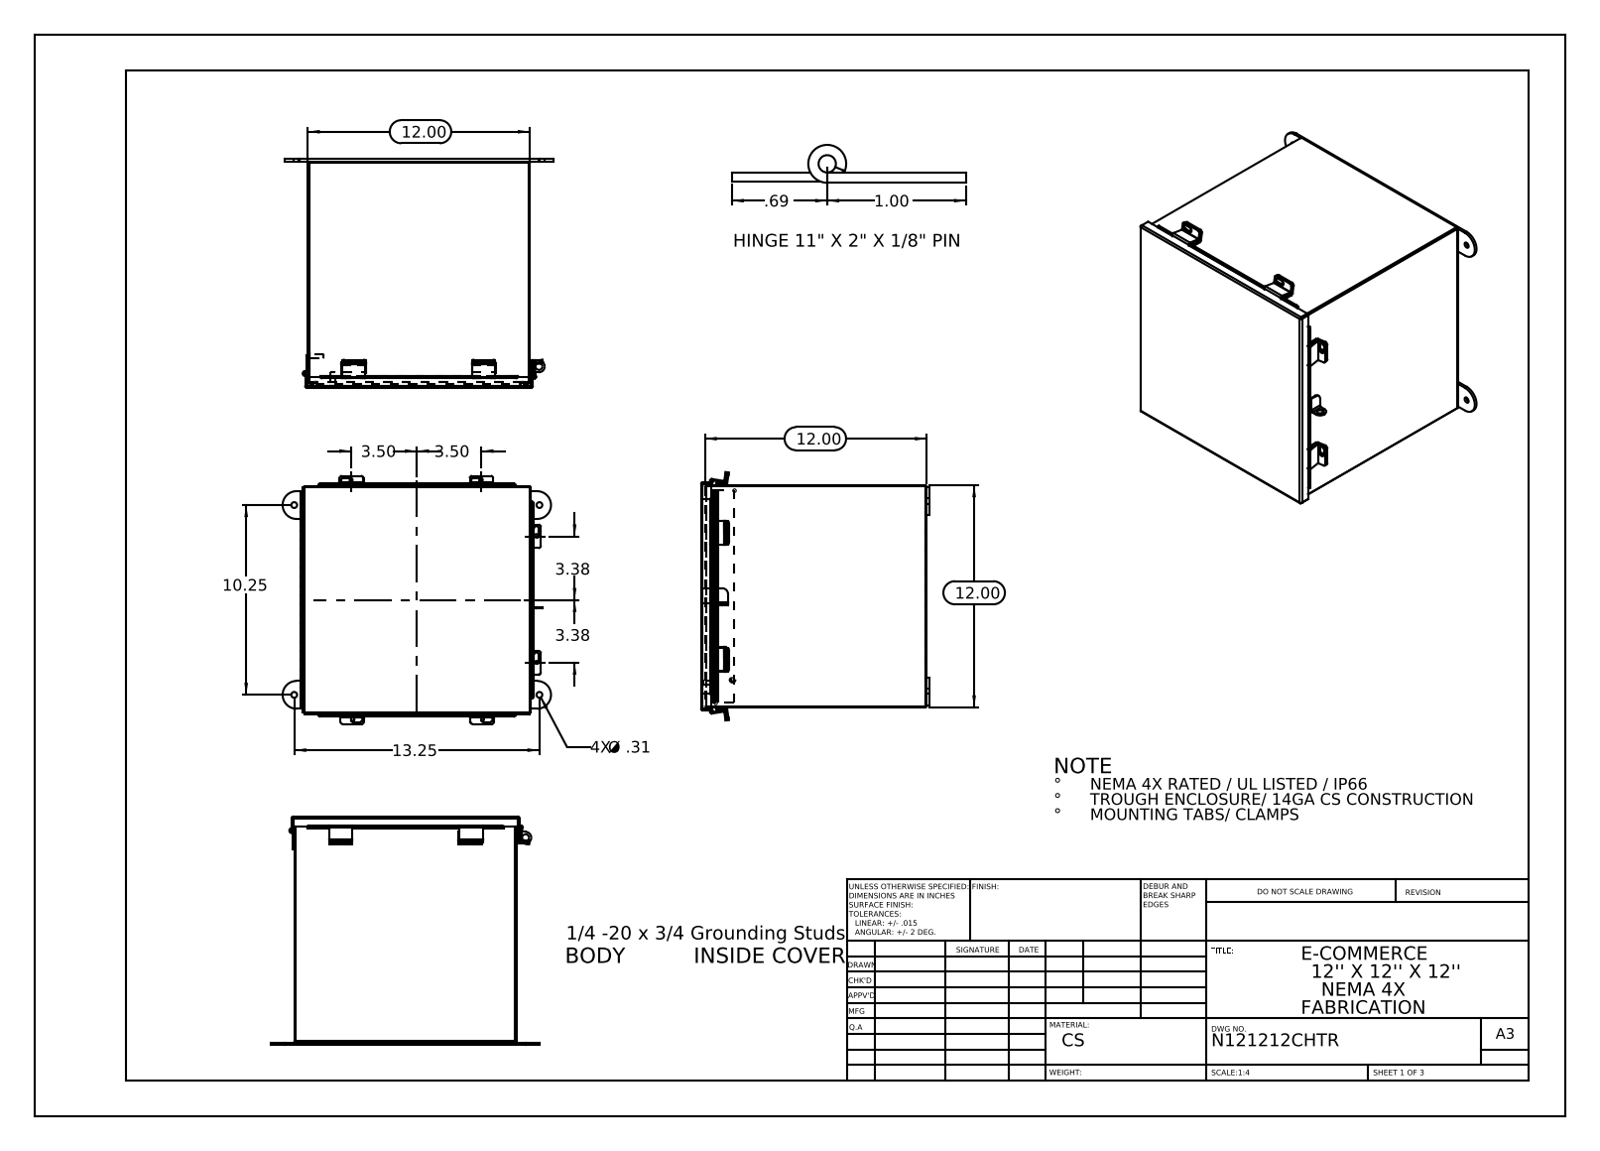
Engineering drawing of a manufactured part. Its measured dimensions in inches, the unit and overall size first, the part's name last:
Units: inches
Overall size (bounding box): 14.5 × 13.407 × 12.337
Round holes (diameter × count): ⌀0.25 ×6, ⌀0.313 ×4, ⌀0.125 ×1, ⌀0.125 ×1, ⌀0.375 ×1
Round bosses / shafts (diameter × count): ⌀0.315 ×2, ⌀0.236 ×2, ⌀0.273 ×1, ⌀0.25 ×1
Partial cylindrical surfaces — rounded edges, fillets, slot ends (radius × count): R0.125 ×24, R0.009 ×12, R0.133 ×12, R0.013 ×10, R0.088 ×10, R0.083 ×6, R0.1 ×6, R0.75 ×4
Main face-to-face distances: 0.075, 11.925, 11.85, 12, 12.128, 12.203, 12.053, 0.135, 0.209, 12.263
Hole centre spacings: 7, 10.25, 13.25, 16.752, 6.85, 12.632
Volume: 76.24 in³ · Surface area: 2 010 in²
Bodies: 23 solids, 728 faces (465 planar, 243 cylindrical, 20 other)
Part name (STEP PRODUCT): N121212SSCHTR Hinge Cover Side JIC; N121212SSCHTR JIC Top; N121212SSCHTR JIC Mounting Bracket; N121212SSCHTR JIC Clamp Bracket (+8 more)
STEP written by: SolidWorks 2013 (CONFIG_CONTROL_DESIGN)
